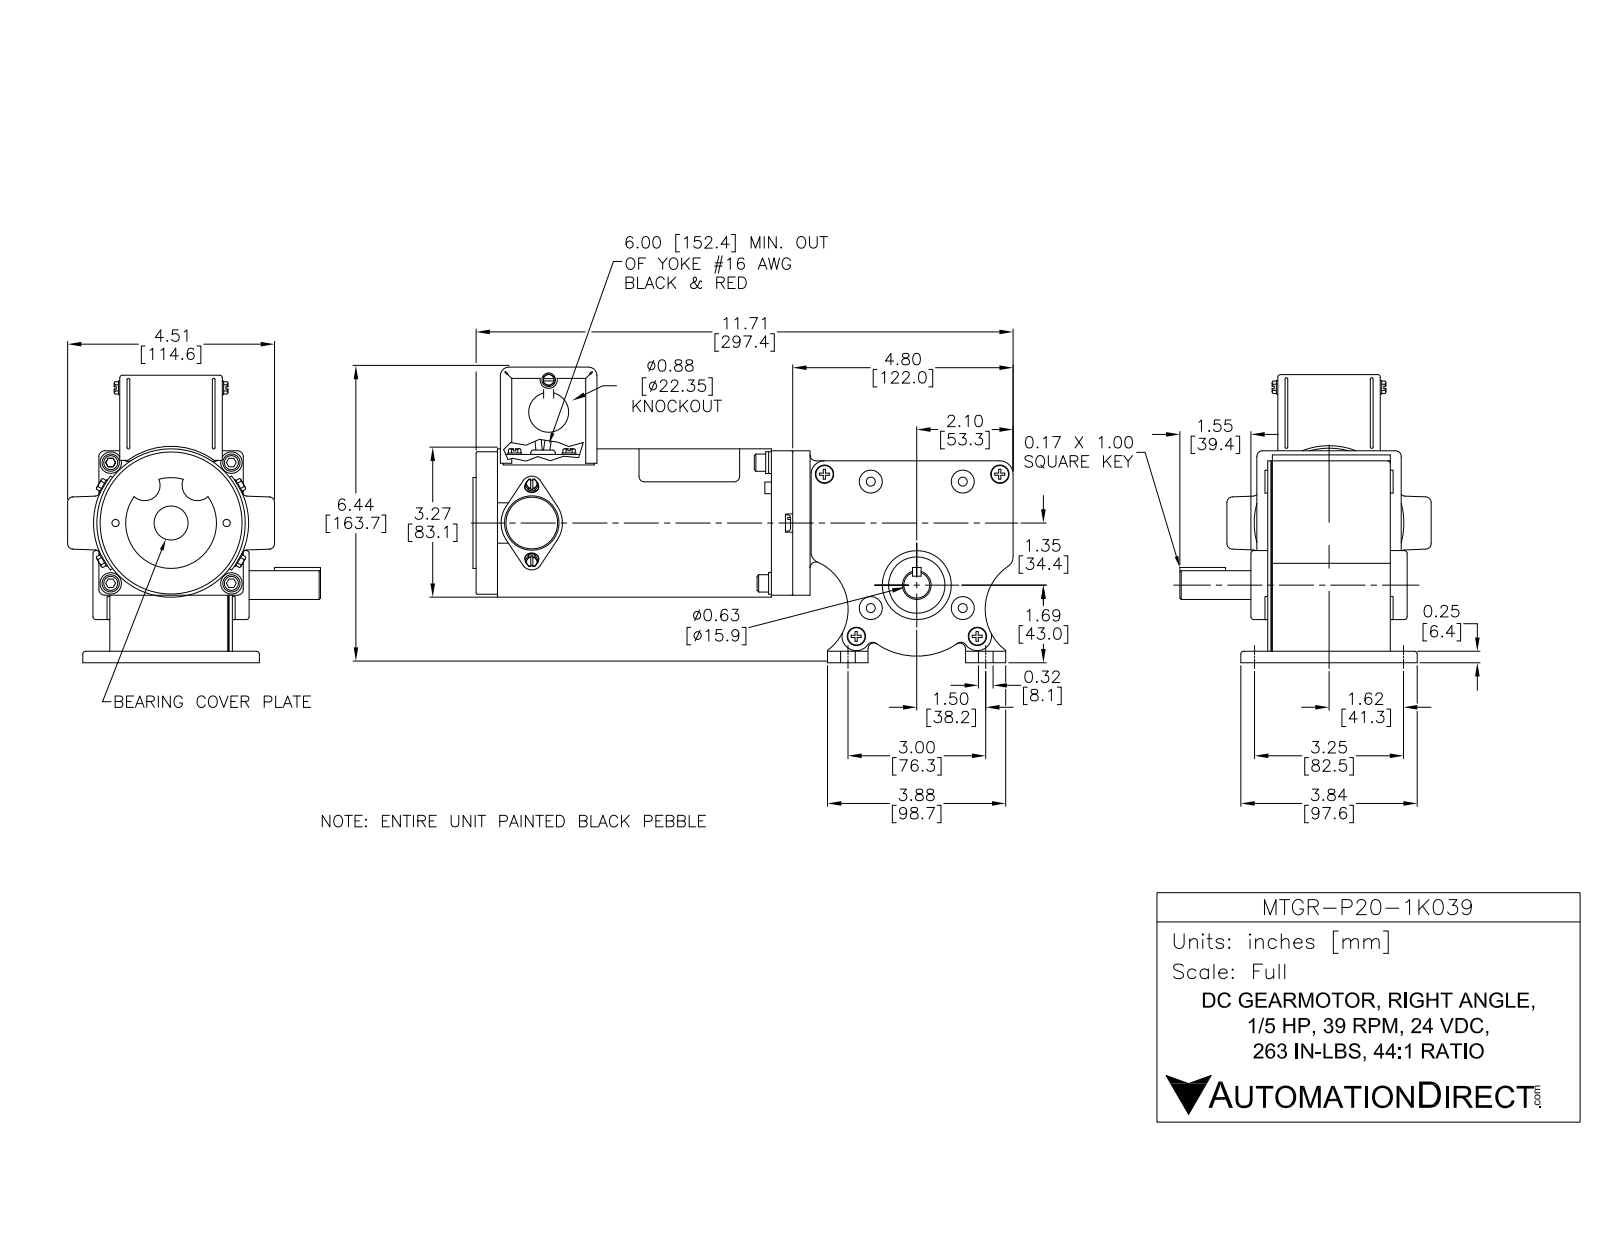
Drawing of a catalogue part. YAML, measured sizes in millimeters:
part_name: "P20-1K040"
step_written_by: "SolidWorks 2013 (AUTOMOTIVE_DESIGN)"
units: millimeters
bodies: {solids: 43, faces: 797, planar: 486, cylindrical: 283, other: 28}
overall_size: [299.5, 165.7, 137.5]
volume: 1059000
surface_area: 306900
round_holes:
  - {diameter: 12.7, count: 5}
  - {diameter: 3.2, count: 4}
  - {diameter: 5, count: 4}
  - {diameter: 10.2, count: 4}
  - {diameter: 5, count: 2}
  - {diameter: 6.4, count: 1}
  - {diameter: 7.6, count: 1}
  - {diameter: 9.5, count: 1}
  - {diameter: 15.9, count: 1}
  - {diameter: 25.4, count: 1}
  - {diameter: 28.6, count: 1}
  - {diameter: 38.1, count: 1}
round_bosses_or_shafts:
  - {diameter: 9.5, count: 6}
  - {diameter: 7.6, count: 4}
  - {diameter: 9.5, count: 3}
  - {diameter: 3.2, count: 2}
  - {diameter: 2.5, count: 2}
  - {diameter: 80.2, count: 1}
  - {diameter: 15.9, count: 1}
  - {diameter: 7.6, count: 1}
partial_cylinders:
  - {radius: 3.2, count: 4}
  - {radius: 4.1, count: 4}
  - {radius: 4.9, count: 4}
  - {radius: 5.9, count: 4}
  - {radius: 6.4, count: 4}
  - {radius: 3.3, count: 2}
  - {radius: 4, count: 2}
  - {radius: 7.4, count: 2}
face_to_face_distances: [0.4, 0.8, 0.8, 66.1, 65.7, 65.4, 2.5, 1.8, 2.2, 67.9]
hole_center_spacings: [33.5, 47.2, 66.8, 72.8, 28.4, 31.2, 50.8, 60.2]
